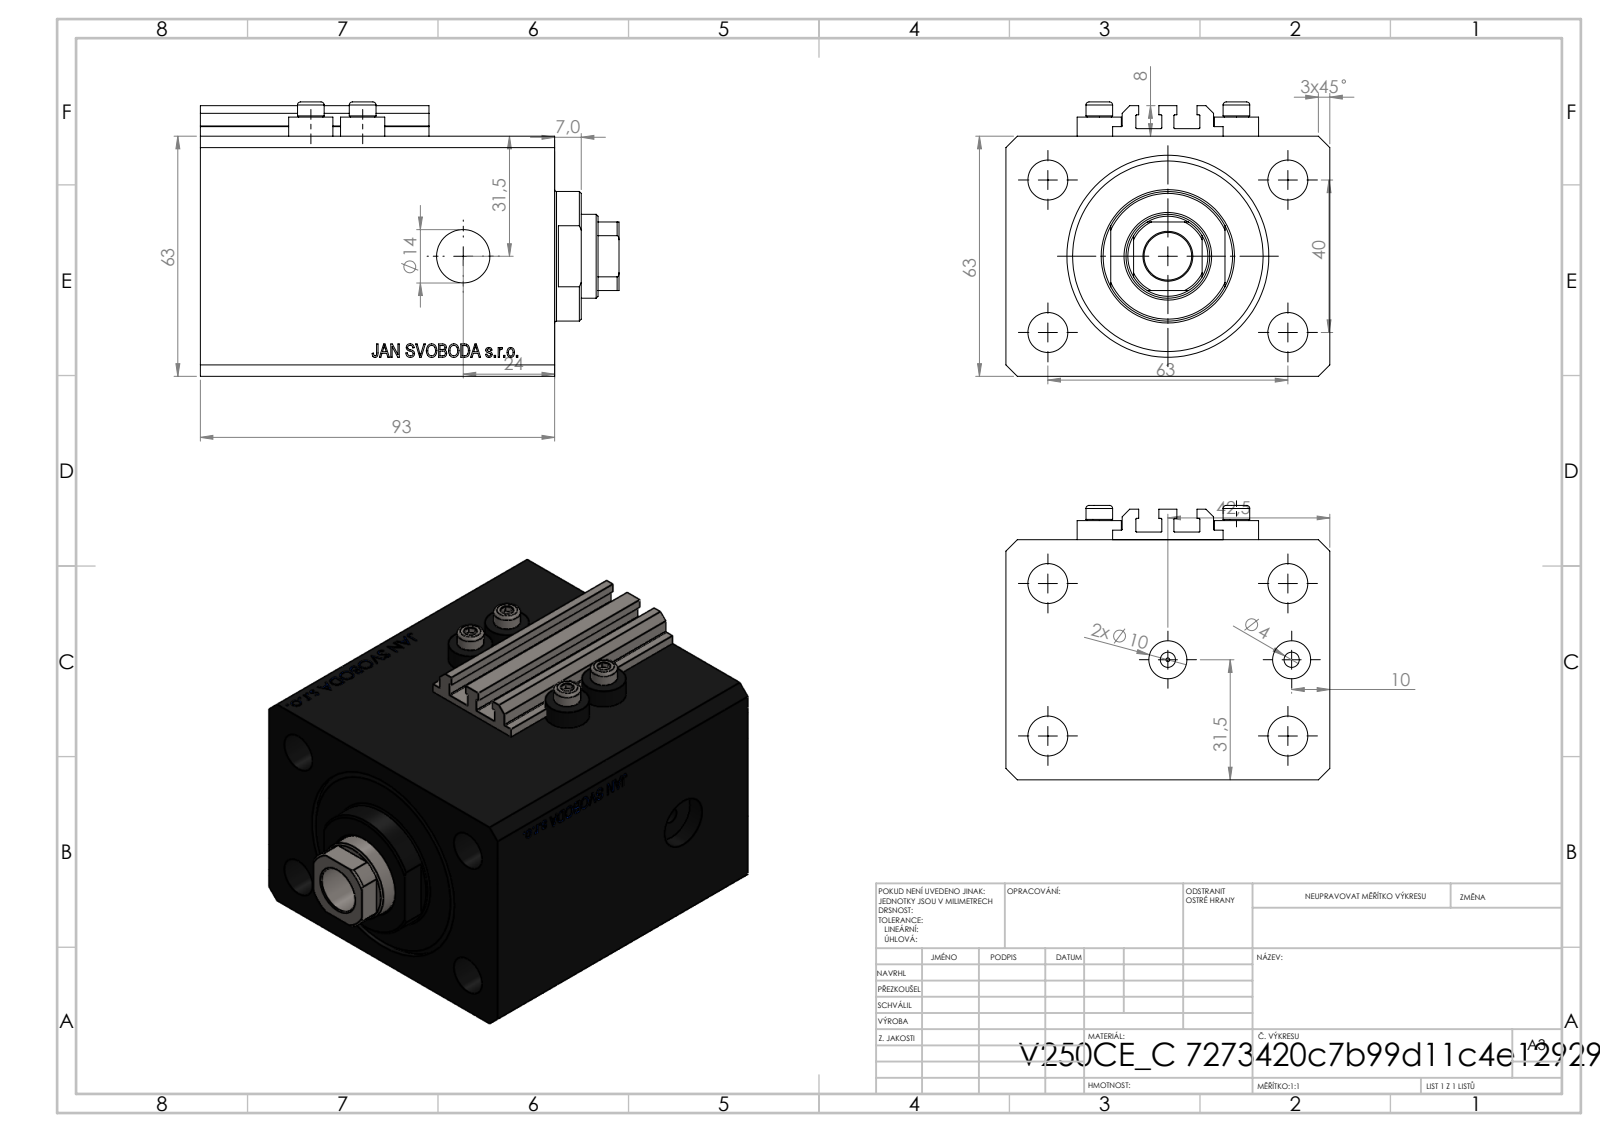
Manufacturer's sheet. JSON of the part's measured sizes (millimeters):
{"part_name": "V250CE_VC_C; ALLEN BOLT V250CE; V250CE_C_VCP; V250CE_C_Body", "step_written_by": "SolidWorks 2019 (CONFIG_CONTROL_DESIGN)", "units": "millimeters", "bodies": {"solids": 8, "faces": 1036, "planar": 504, "cylindrical": 86, "other": 446}, "overall_size": [109.9, 85, 72], "volume_mm3": 459843, "surface_area_mm2": 94695, "round_holes": [[4, 7], [10.5, 4], [10, 2], [14, 2], [1.25, 1], [12.5, 1], [22, 1], [40, 1], [53, 1]], "round_bosses_or_shafts": [[11.6, 4], [7, 4], [34, 1]], "partial_cylinders_radius": [[0.2, 10], [10.5, 1]], "face_to_face_distances": [63, 85, 93, 54.5, 65.9, 27.1, 11.4, 81.6, 3, 2.5], "hole_center_spacings": [37.31, 13.6, 20.02, 36, 38.48, 40, 63, 67.05]}
